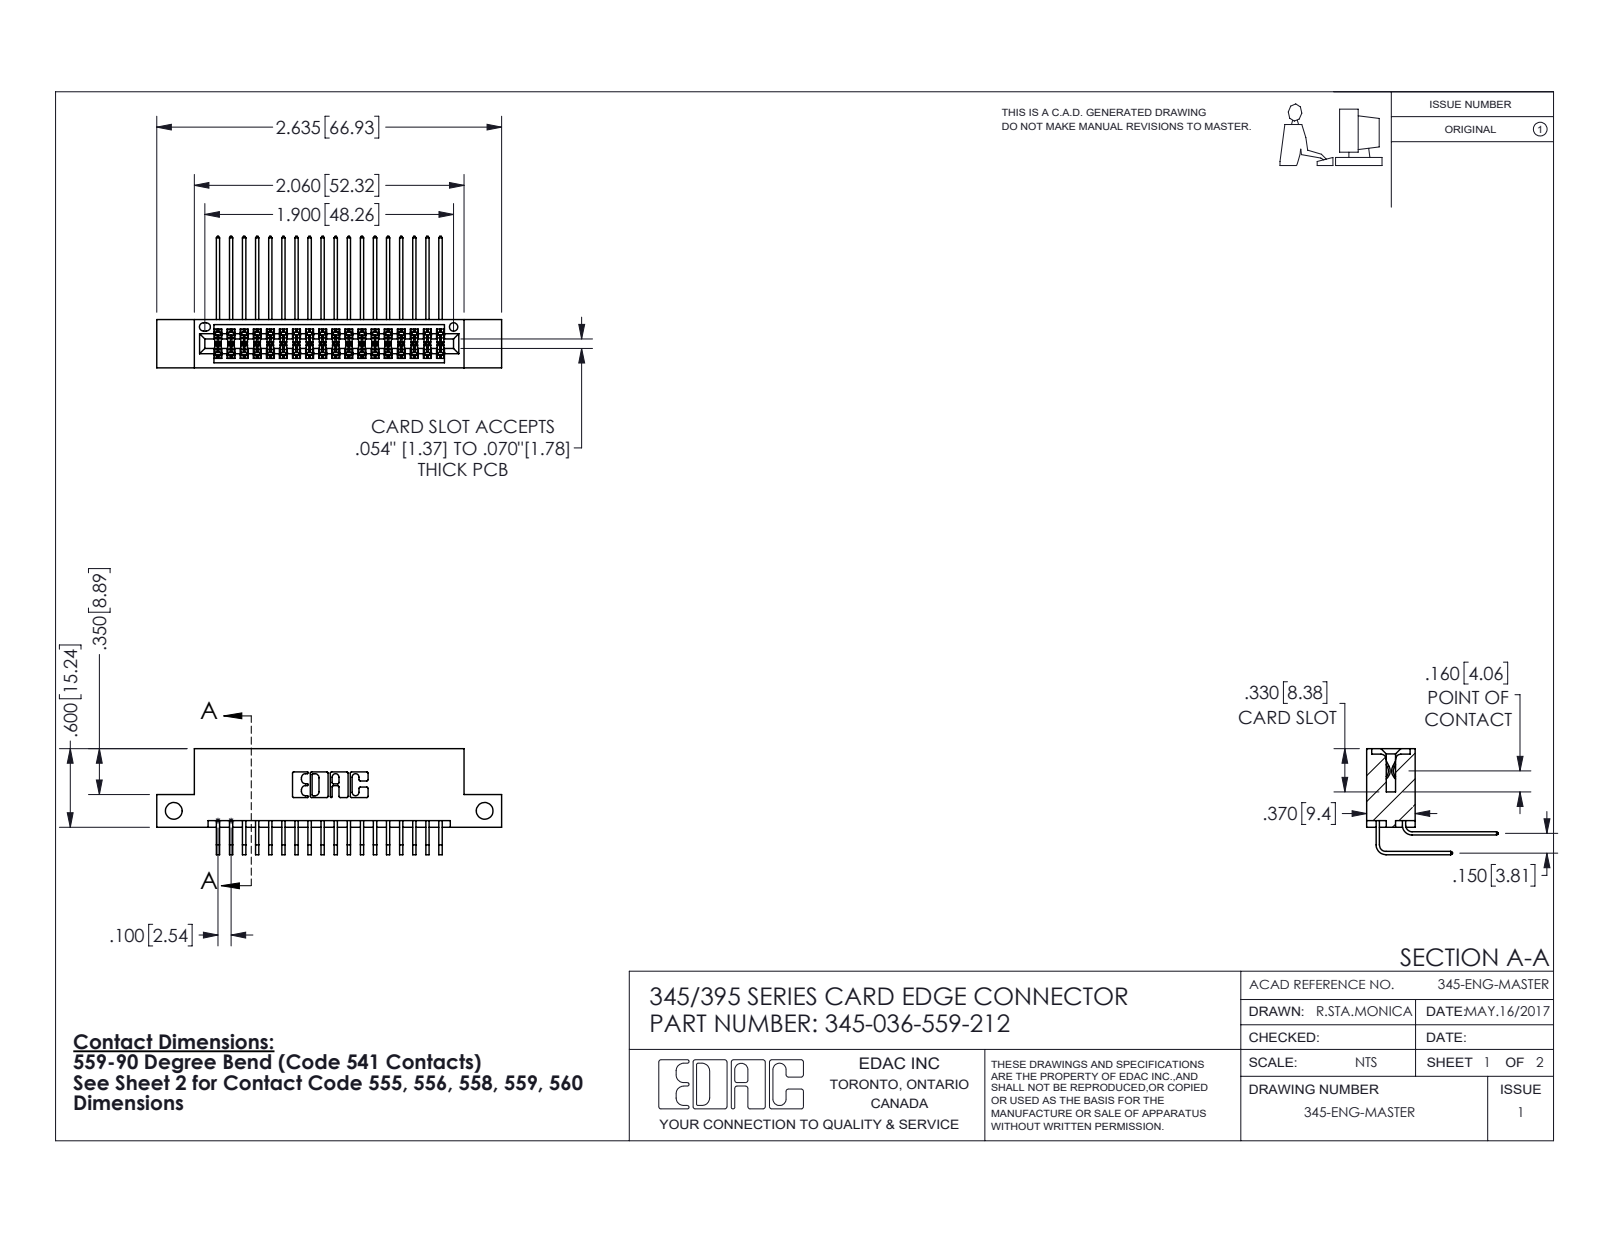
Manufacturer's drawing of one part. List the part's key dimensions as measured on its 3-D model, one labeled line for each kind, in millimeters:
Part name (STEP PRODUCT): 345-292-001_558 559 Tail - 1; 345 Part_Flush Mounting Lugs - Side Mount; 345-036-559-212; 345-292-001_559 Tail - 2
STEP written by: SolidWorks 2016 (CONFIG_CONTROL_DESIGN)
Units: millimetres
Bodies: 37 solids, 1998 faces (1340 planar, 658 cylindrical, 0 other)
Overall size (bounding box): 66.9 × 25.5 × 20.5
Volume: 6 410 mm³ · Surface area: 9 832 mm²
Round holes (diameter × count): ⌀3.3 ×2, ⌀1.6 ×1
Partial cylindrical surfaces — rounded edges, fillets, slot ends (radius × count): R0.2 ×72, R0.3 ×22, R0.2 ×6, R0.8 ×6, R0.7 ×3, R0.4 ×2, R0.5 ×2, R0.6 ×2
Main face-to-face distances: 5.1, 1.8, 7.6, 9.4, 2.5, 6.9, 0.6, 5.7, 3.8, 4.4
Hole centre spacings: 60.3
